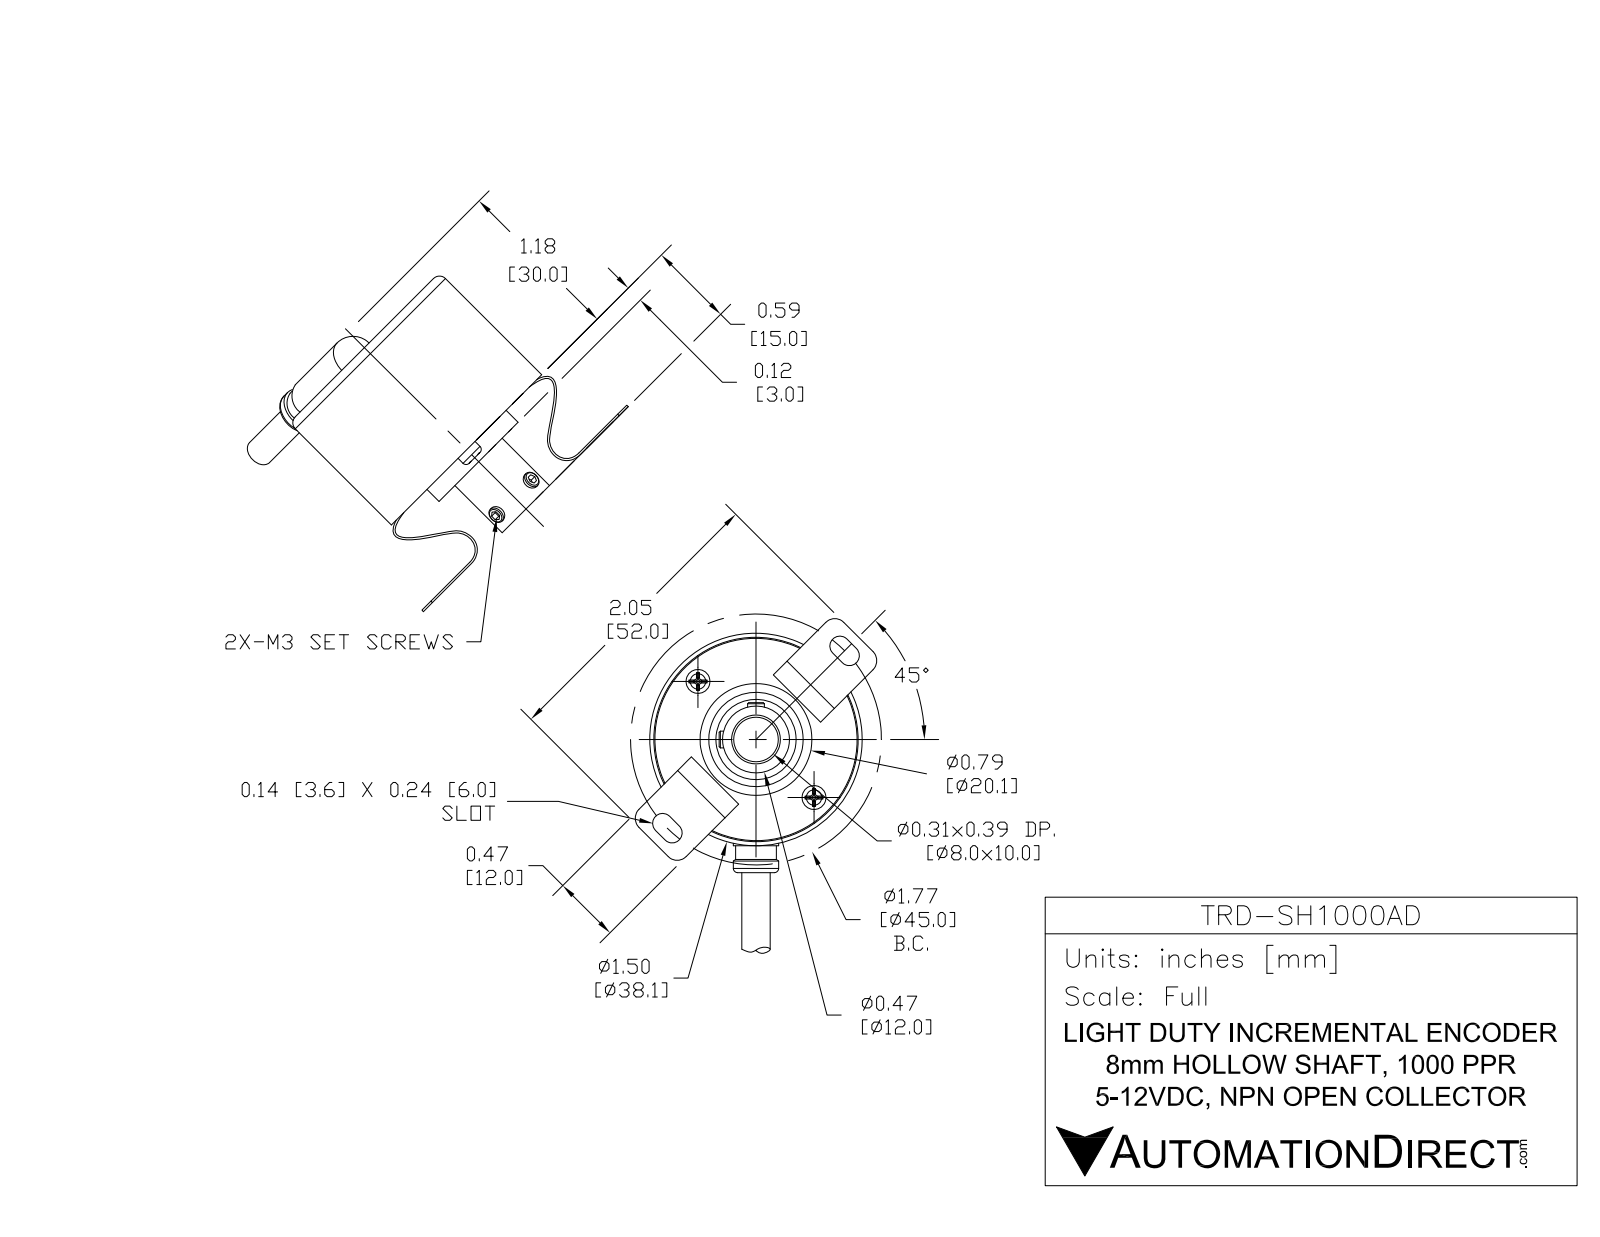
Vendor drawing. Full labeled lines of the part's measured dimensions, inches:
Part name (STEP PRODUCT): TRD-SH1000AD
STEP written by: SolidWorks 2016 (AUTOMOTIVE_DESIGN)
Units: inches
Bodies: 11 solids, 322 faces (169 planar, 101 cylindrical, 52 other)
Overall size (bounding box): 3.952 × 1.772 × 1.684
Volume: 2.043 in³ · Surface area: 17.32 in²
Round holes (diameter × count): ⌀0.126 ×5, ⌀0.098 ×2, ⌀0.315 ×1, ⌀0.791 ×1
Round bosses / shafts (diameter × count): ⌀0.118 ×5, ⌀1.496 ×1, ⌀0.787 ×1, ⌀0.591 ×1, ⌀0.472 ×1, ⌀0.299 ×1, ⌀0.197 ×1, ⌀0.134 ×1
Partial cylindrical surfaces — rounded edges, fillets, slot ends (radius × count): R0.039 ×6, R0.118 ×5, R0.03 ×4, R0.071 ×4, R0.087 ×4, R0.098 ×4, R0.031 ×2, R0.146 ×2
Main face-to-face distances: 1.024, 0.579, 1.035, 0.591, 1.614, 1.602, 0.567, 0.118, 1.142, 0.106
Hole centre spacings: 0.551, 0.78, 0.955, 0.285, 0.285, 0.954, 1.065, 1.065
